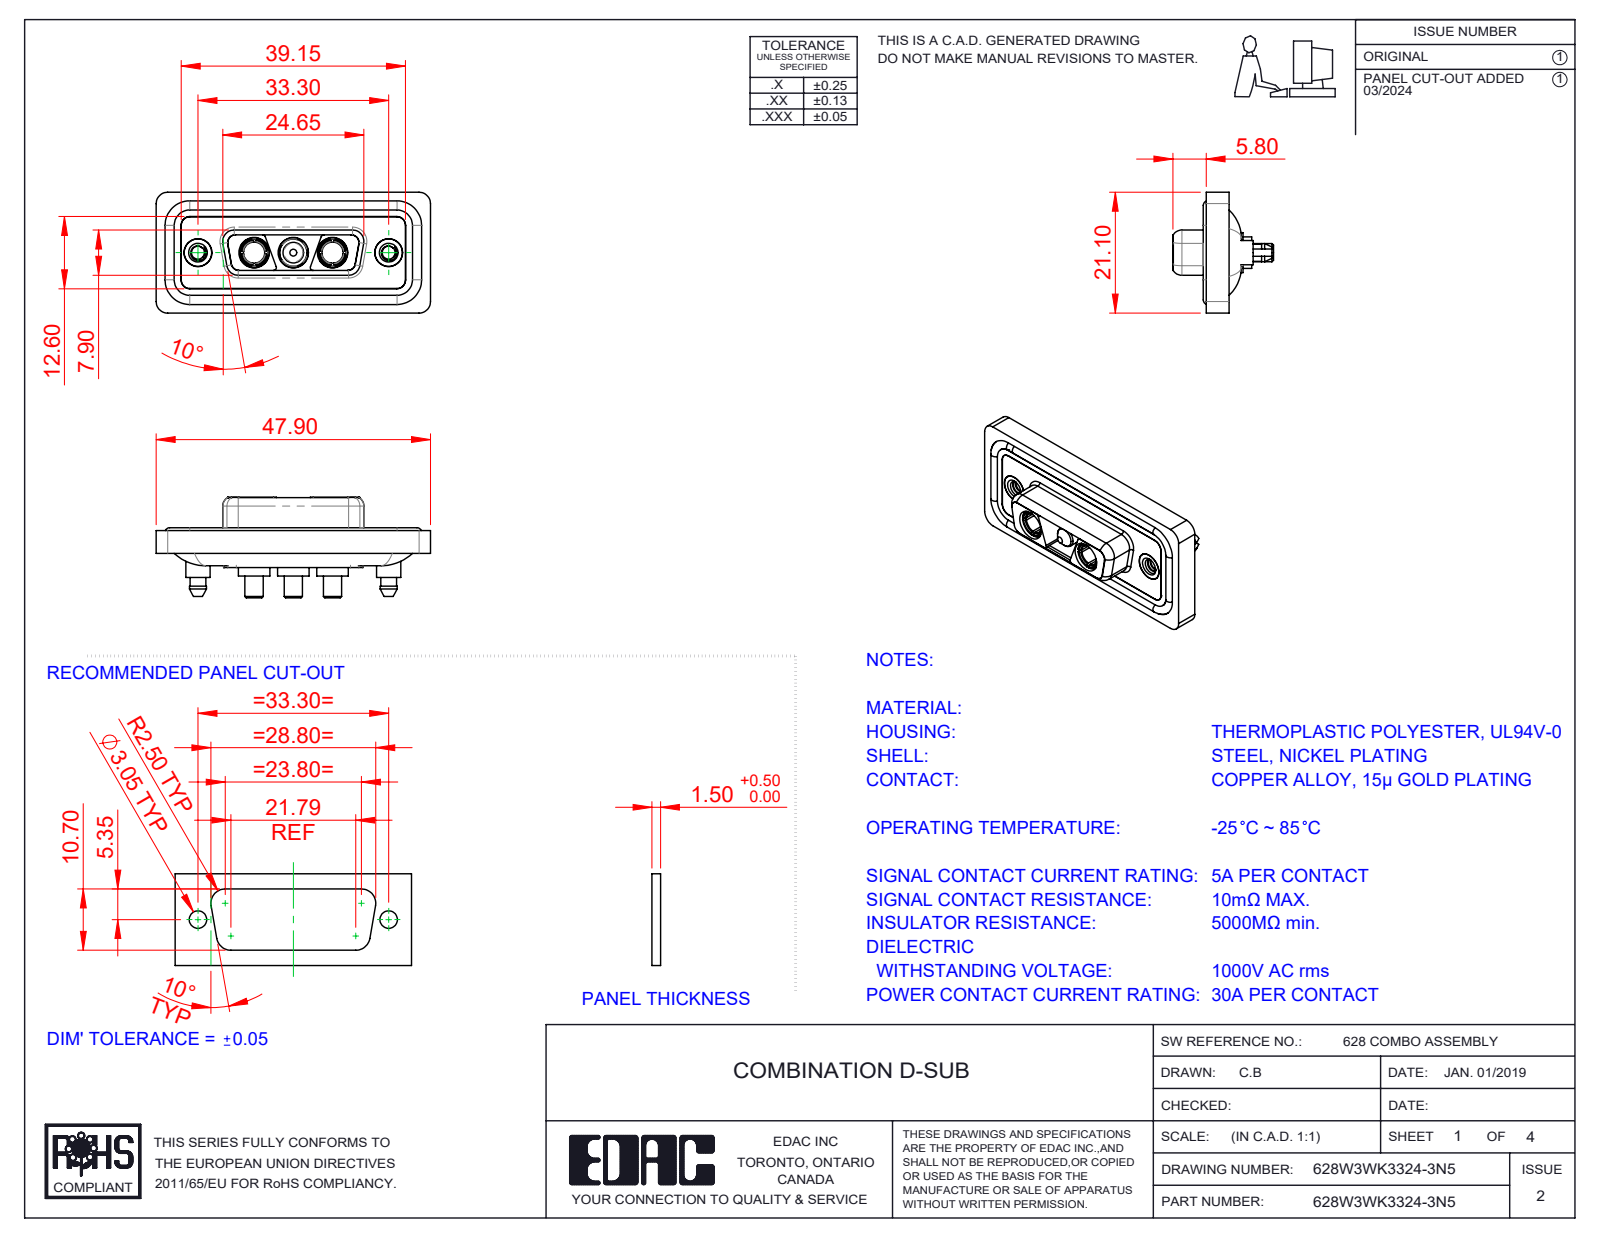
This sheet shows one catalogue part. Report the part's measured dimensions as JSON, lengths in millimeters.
{"part_name": "628Combo Threaded Boardlock_5; Power Socket_30A S; 628Combo Housing_3WK3; 628Combo Shell Front_15 Contacts (+4 more)", "step_written_by": "SolidWorks 2023 (CONFIG_CONTROL_DESIGN)", "units": "millimeters", "bodies": {"solids": 13, "faces": 633, "planar": 194, "cylindrical": 290, "other": 149}, "overall_size": [47.9, 21.1, 17.55], "volume_mm3": 6033, "surface_area_mm2": 9852, "round_holes": [[4.85, 5], [5.3, 3], [2.26, 2], [3.7, 2], [4, 2], [4.05, 2], [5, 2]], "round_bosses_or_shafts": [[1.6, 4], [5.5, 3], [5.2, 3], [4.75, 3], [3.75, 3], [3.2, 3], [5.4, 2], [4.96, 2]], "partial_cylinders_radius": [[1.5, 24], [2, 20], [1.35, 12], [1.6, 10], [0.5, 8], [0.25, 4], [0.6, 4], [0.65, 4]], "face_to_face_distances": [0.4, 1.6, 1.8, 0.5, 1.1, 2.9, 5.65, 7.05, 1.5, 5.35], "hole_center_spacings": [6.85, 9.8, 16.65, 23.5, 13.7, 33.3]}
